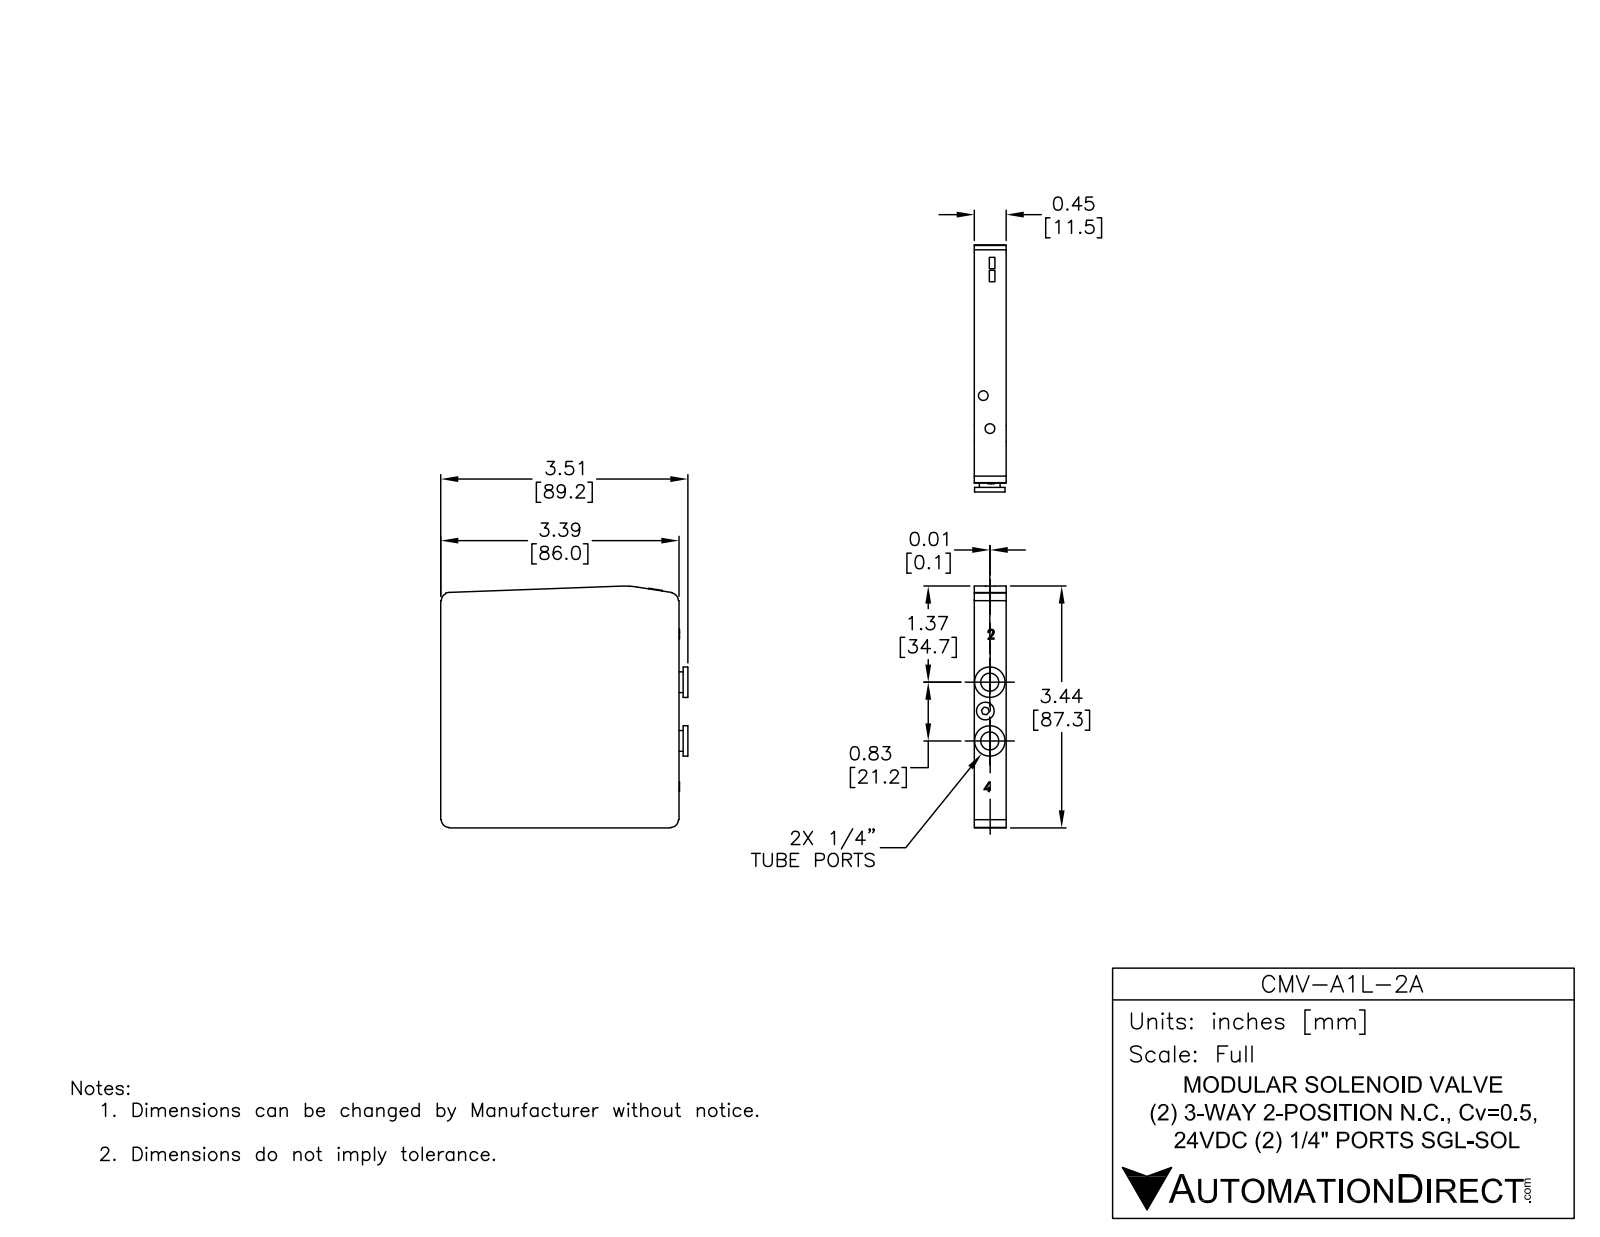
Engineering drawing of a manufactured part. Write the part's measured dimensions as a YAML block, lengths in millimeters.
part_name: "CMV-A1L-2A"
step_written_by: "SolidWorks 2013 (AUTOMOTIVE_DESIGN)"
units: millimeters
bodies: {solids: 78, faces: 1139, planar: 883, cylindrical: 162, other: 94}
overall_size: [89.5, 87.3, 20.43]
volume: 78068
surface_area: 44221
round_holes:
  - {diameter: 5.25, count: 4}
  - {diameter: 6.5, count: 4}
  - {diameter: 3.35, count: 2}
  - {diameter: 4.4, count: 2}
  - {diameter: 8, count: 2}
  - {diameter: 9.5, count: 2}
  - {diameter: 3.6, count: 1}
  - {diameter: 6.25, count: 1}
  - {diameter: 6.4, count: 1}
round_bosses_or_shafts:
  - {diameter: 1.5, count: 4}
  - {diameter: 10.8, count: 2}
  - {diameter: 7.75, count: 2}
  - {diameter: 6.25, count: 2}
  - {diameter: 5.75, count: 2}
  - {diameter: 4.2, count: 2}
  - {diameter: 4, count: 2}
  - {diameter: 3.5, count: 1}
partial_cylinders:
  - {radius: 2.35, count: 12}
  - {radius: 0.78, count: 4}
  - {radius: 1.5, count: 4}
  - {radius: 2.8, count: 4}
  - {radius: 0.15, count: 2}
  - {radius: 0.25, count: 2}
  - {radius: 1, count: 2}
  - {radius: 2.25, count: 2}
face_to_face_distances: [11.5, 1.5, 10, 1, 3, 83, 2.5, 12.5, 10.83, 11.83]
hole_center_spacings: [9.7, 19.83, 22.17, 8.66, 8.68, 9.46, 10.38, 10.63]
